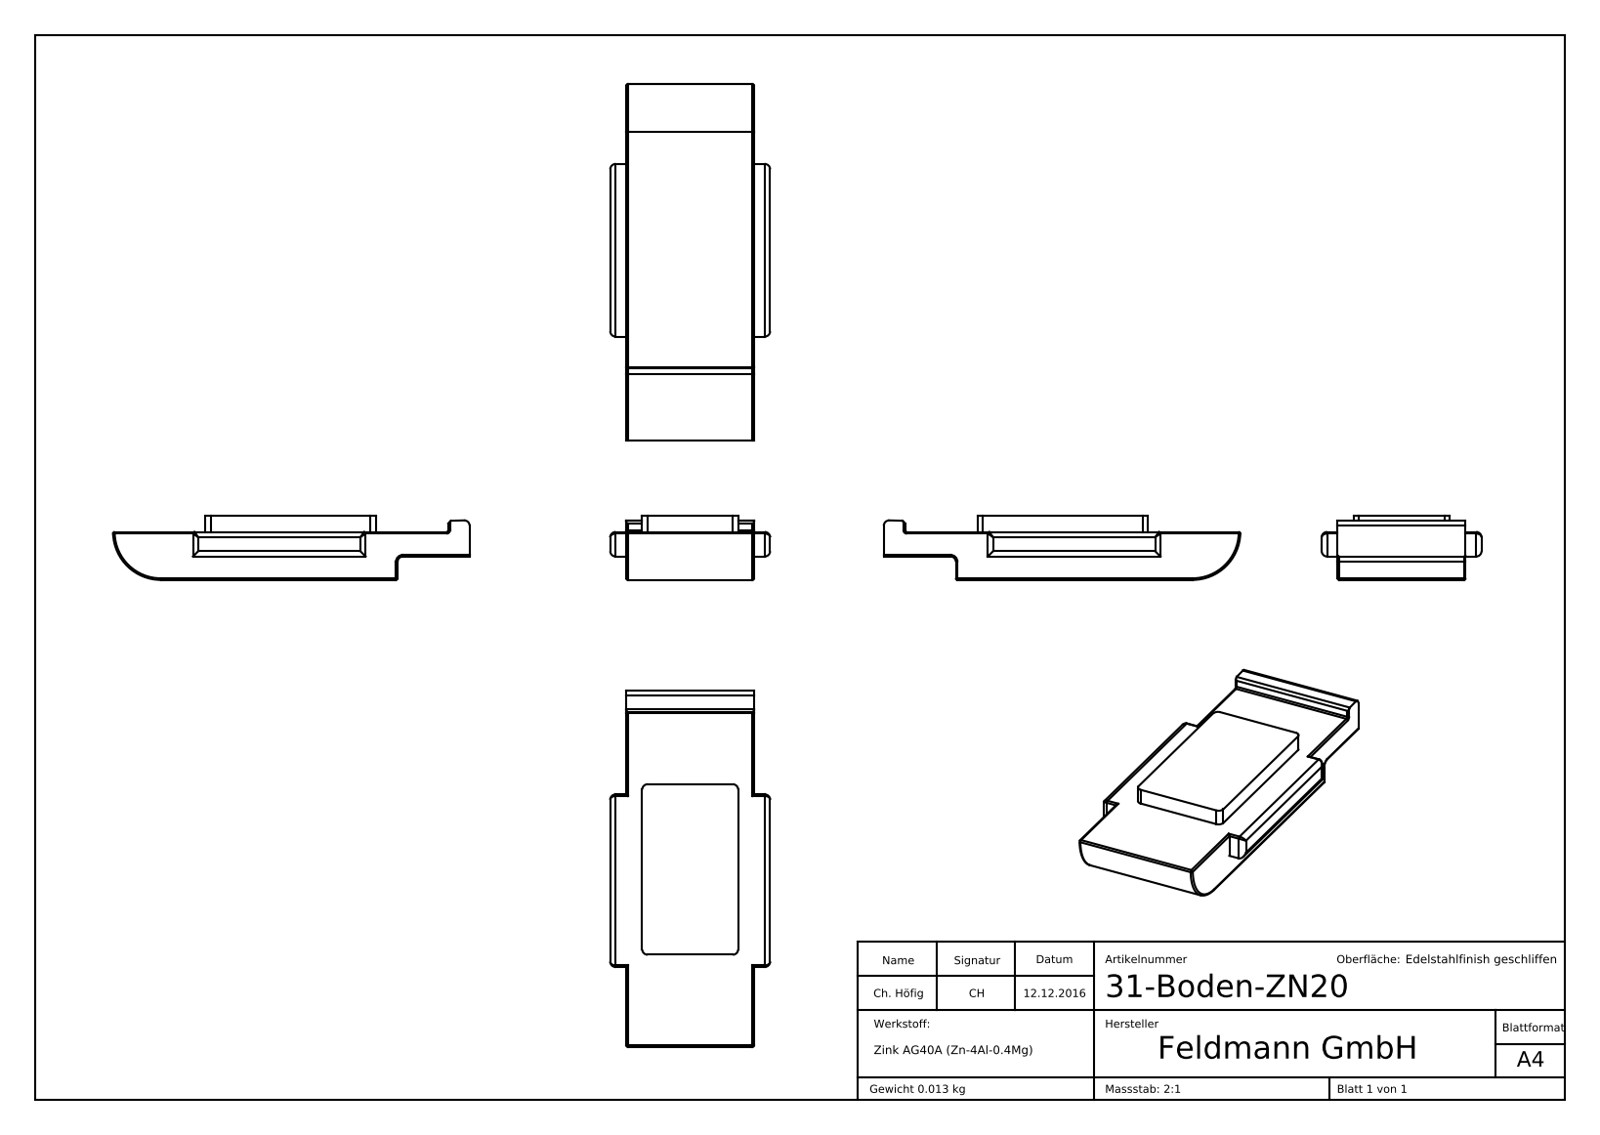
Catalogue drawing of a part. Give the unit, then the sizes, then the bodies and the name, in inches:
Units: inches
Overall size (bounding box): 1.317 × 0.591 × 0.236
Partial cylindrical surfaces — rounded edges, fillets, slot ends (radius × count): R0.006 ×15, R0.02 ×14, R0.177 ×1
Main face-to-face distances: 0.177, 0.059, 0.236, 0.472, 0.087, 0.091, 0.15, 0.413, 0.118, 0.531
Volume: 0.117 in³ · Surface area: 2.065 in²
Bodies: 1 solid, 71 faces (23 planar, 34 cylindrical, 14 other)
Part name (STEP PRODUCT): 31-BODEN-ZN20
STEP written by: SolidWorks 2018 (CONFIG_CONTROL_DESIGN)
